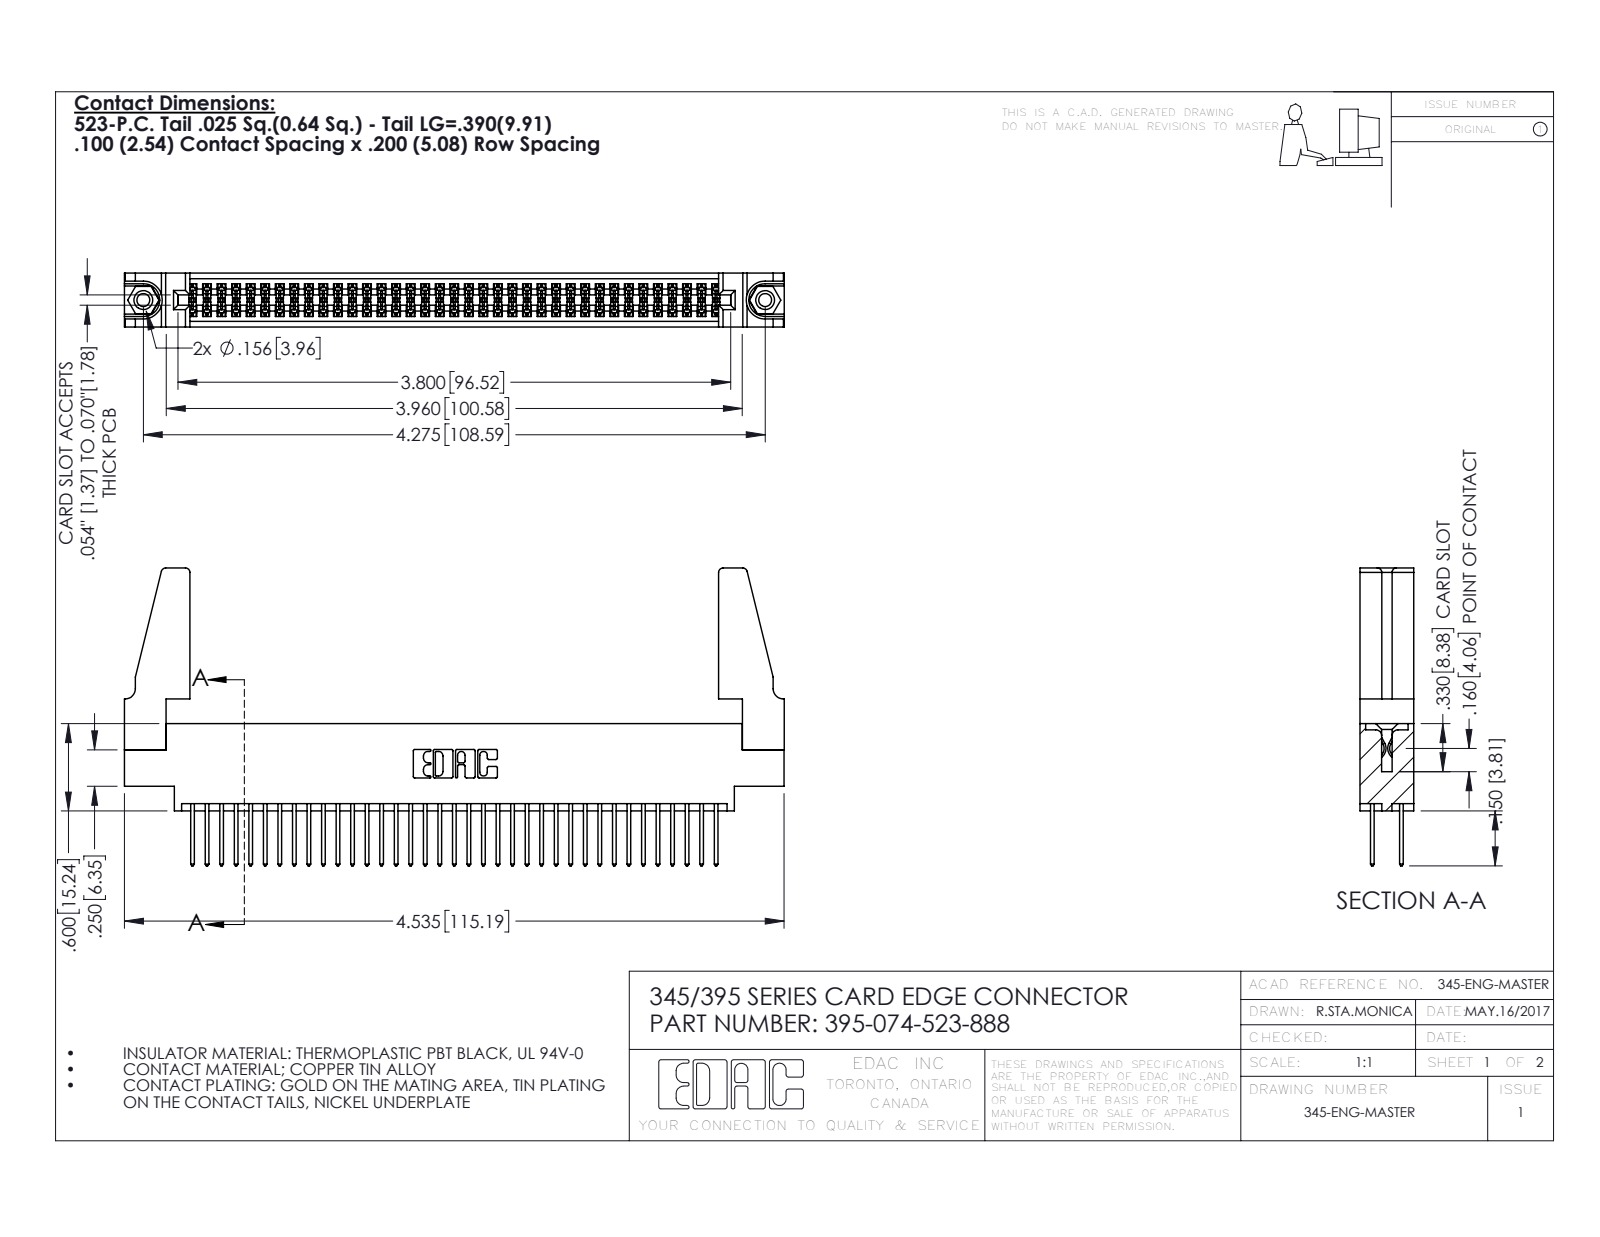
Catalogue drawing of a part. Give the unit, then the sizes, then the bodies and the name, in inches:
Units: inches
Overall size (bounding box): 4.536 × 2.047 × 0.37
Round holes (diameter × count): ⌀0.089 ×2, ⌀0.125 ×2, ⌀0.156 ×2, ⌀0.064 ×1
Round bosses / shafts (diameter × count): ⌀0.155 ×2
Partial cylindrical surfaces — rounded edges, fillets, slot ends (radius × count): R0.006 ×111, R0.01 ×74, R0.01 ×22, R0.03 ×8, R0.007 ×6, R0.031 ×6, R0.026 ×3, R0.014 ×2
Main face-to-face distances: 0.072, 0.298, 0.37, 0.098, 0.272, 0.025, 0.2, 0.225, 0.175, 0.149
Hole centre spacings: 0.27, 4.039, 4.275
Volume: 0.881 in³ · Surface area: 31.59 in²
Bodies: 79 solids, 3954 faces (2598 planar, 1340 cylindrical, 16 other)
Part name (STEP PRODUCT): 345-220-078_345-220-088; 345 Part_0.170 Offset - 0.156 Dia-TH; 345-292-001_345-293-123; 395-074-523-888 (+1 more)
STEP written by: SolidWorks 2016 (CONFIG_CONTROL_DESIGN)
